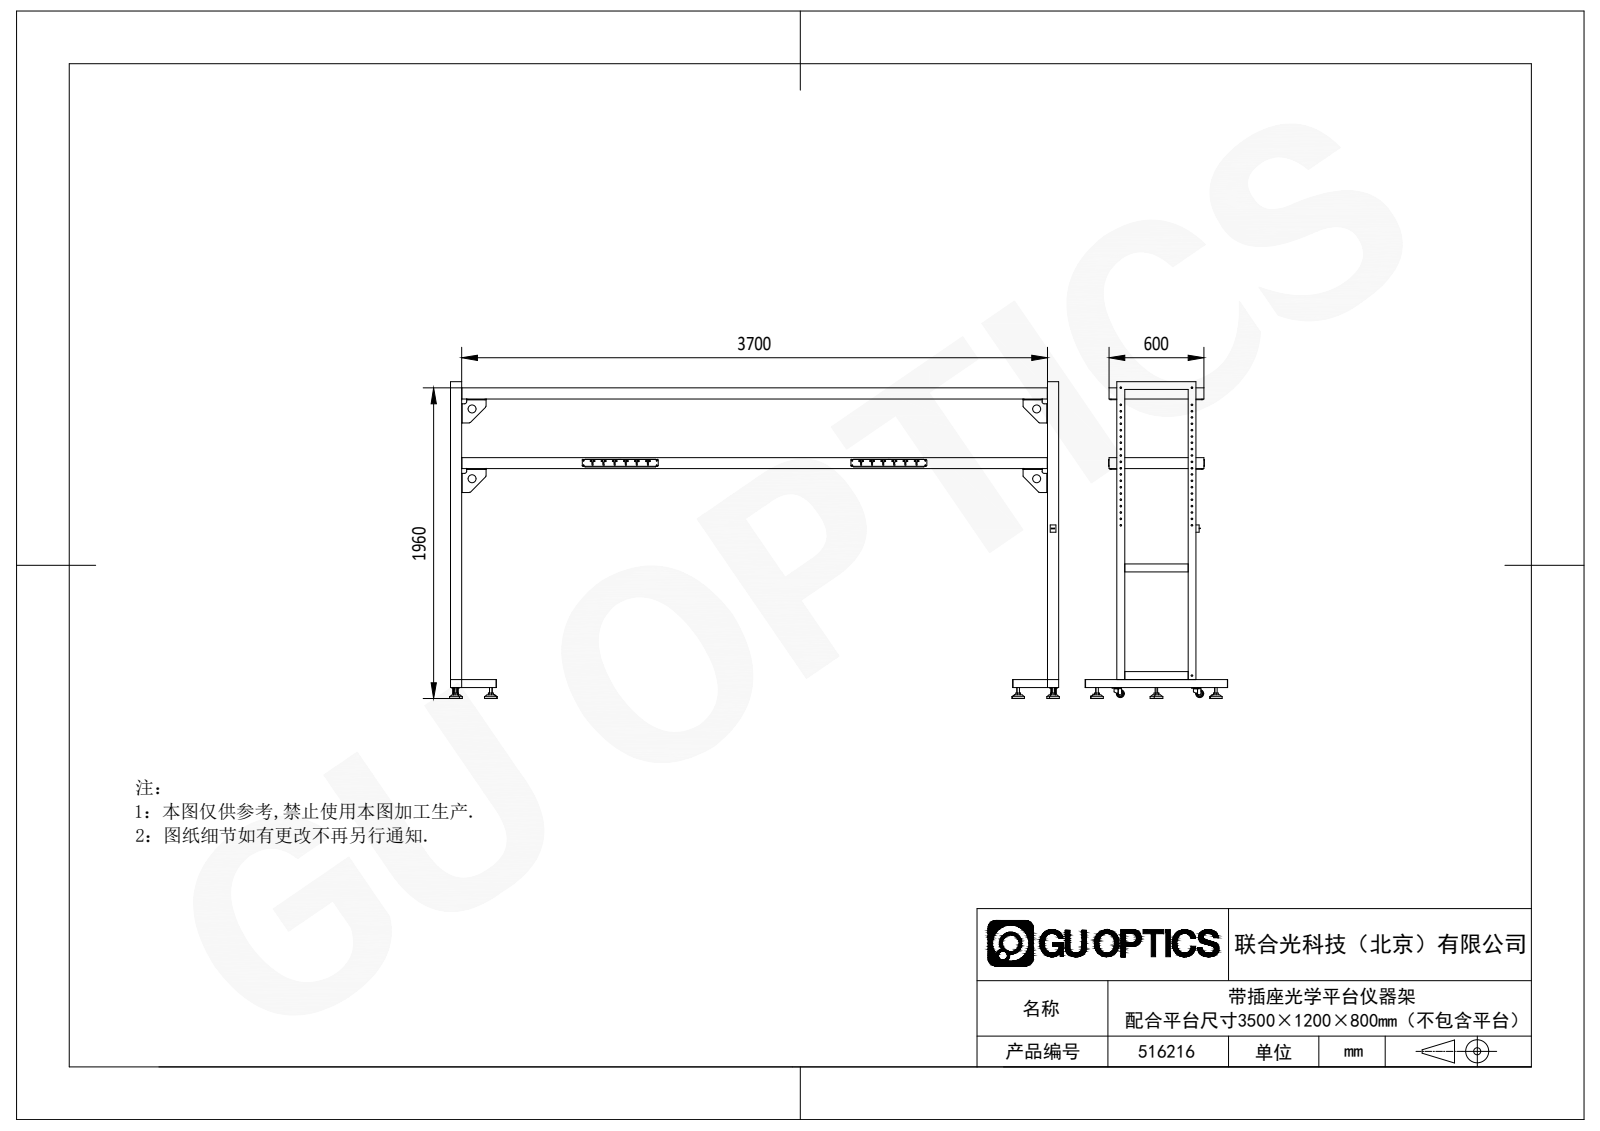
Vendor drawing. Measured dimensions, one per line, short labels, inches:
name: 516216
written by: SolidWorks 2020 (CONFIG_CONTROL_DESIGN)
unit: in
bodies: 55 solids, 2593 faces (1445 planar, 1072 cylindrical, 76 other)
size: 151.575 × 78.78 × 35.433
volume: 1 844 in³; area: 34 690 in²
holes: 66× ⌀0.354, 16× ⌀0.24, 16× ⌀0.394, 12× ⌀0.256, 8× ⌀0.165, 8× ⌀0.205, 8× ⌀0.236, 6× ⌀0.669, 6× ⌀0.709, 6× ⌀1.024, 6× ⌀2.717, 4× ⌀0.126
bosses: 6× ⌀3.15, 6× ⌀0.63, 4× ⌀1.024, 4× ⌀0.709, 2× ⌀1.969, 2× ⌀0.394
rounds: 36× R0.197, 24× R0.276, 16× R0.118, 12× R0.167, 8× R0.059, 8× R0.059, 8× R0.158, 4× R0.512
face distances: 17.323, 0.059, 0.118, 2.756, 2.638, 17.264, 0.098, 2.657, 0.079, 17.382
hole spacings: 1.575, 3.15, 4.724, 11.024, 6.299, 7.874, 9.449, 12.598
